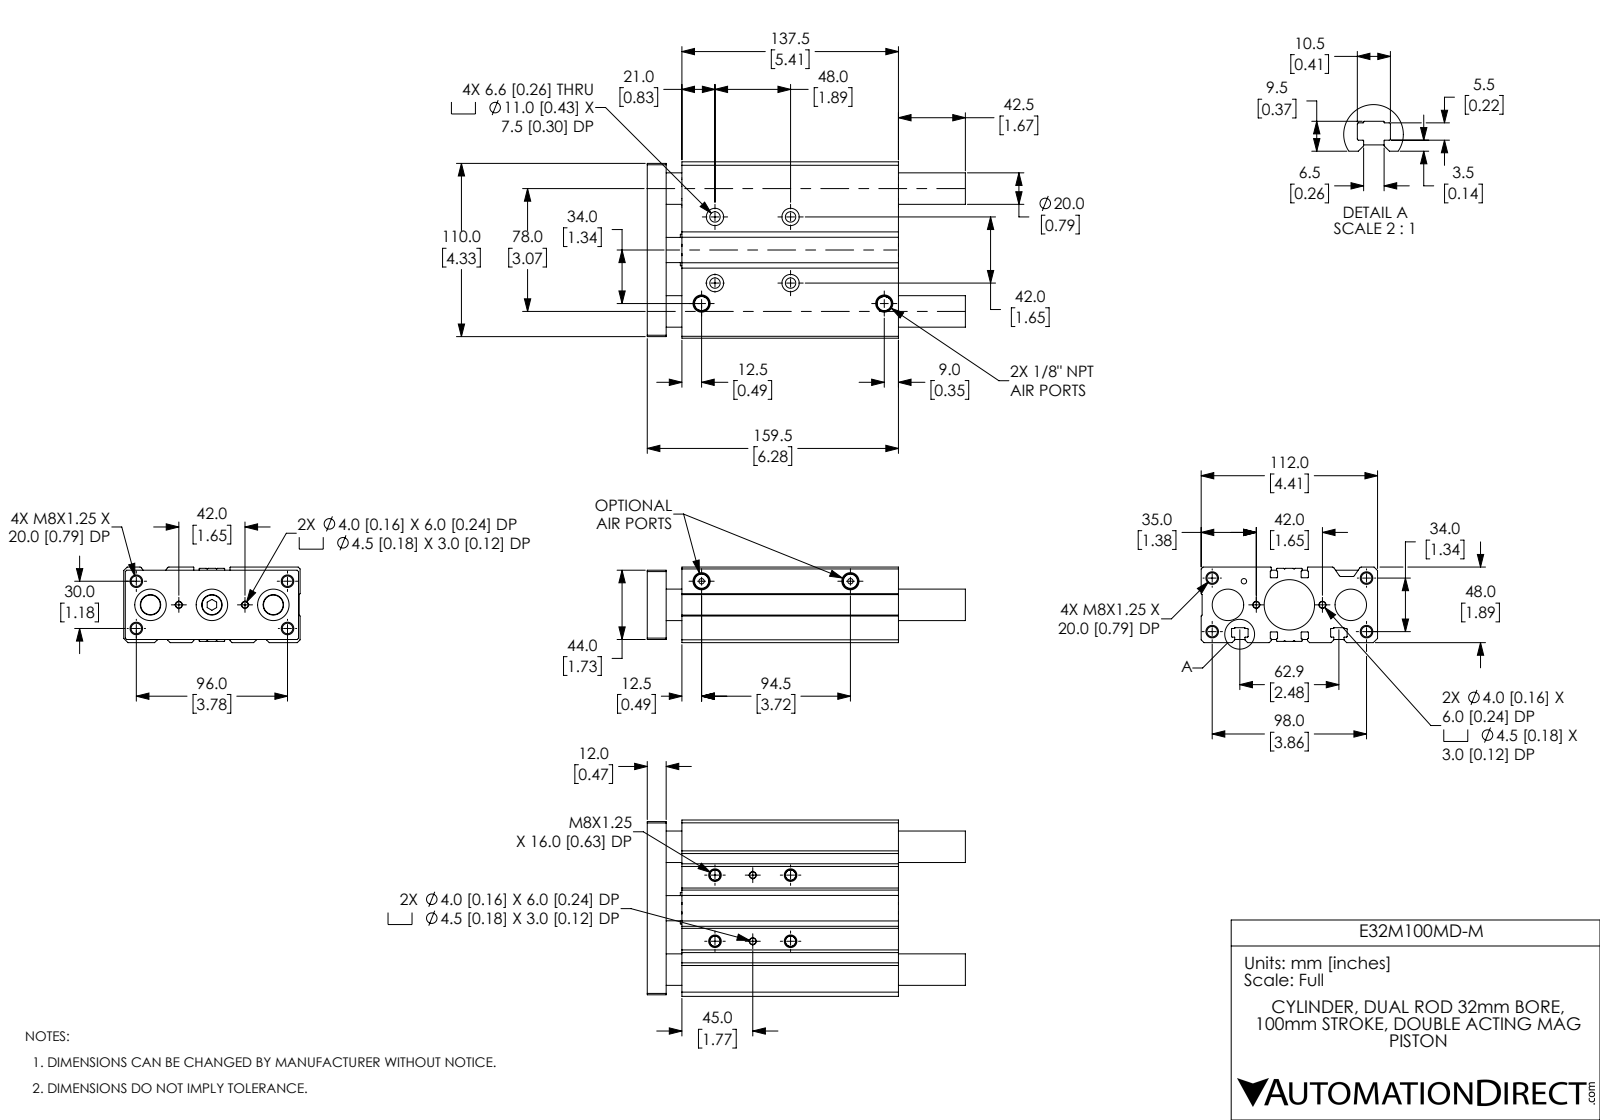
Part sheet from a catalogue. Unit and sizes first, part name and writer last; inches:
Units: inches
Overall size (bounding box): 7.953 × 4.409 × 1.89
Round holes (diameter × count): ⌀0.262 ×12, ⌀0.157 ×4, ⌀0.177 ×4, ⌀0.26 ×4, ⌀0.433 ×4, ⌀0.394 ×3, ⌀0.787 ×3, ⌀0.135 ×2, ⌀0.51 ×2, ⌀0.135 ×1, ⌀0.787 ×1, ⌀1.26 ×1
Round bosses / shafts (diameter × count): ⌀0.63 ×1, ⌀0.51 ×1
Partial cylindrical surfaces — rounded edges, fillets, slot ends (radius × count): R0.008 ×32, R0.016 ×28, R0.047 ×4, R0.012 ×2
Main face-to-face distances: 1.89, 0.236, 0.031, 4.409, 0.866, 0.472, 0.394, 1.858, 0.079, 6.28
Hole centre spacings: 0.088, 0.689, 0.776, 0.945, 1.216, 1.261, 1.29, 1.654
Volume: 42.39 in³ · Surface area: 246.8 in²
Bodies: 5 solids, 423 faces (139 planar, 190 cylindrical, 94 other)
Part name (STEP PRODUCT): E32M100MD-M_BODY; E32M100MD-M; E32M100MD-M_ENDPLATE
STEP written by: SolidWorks 2019 (CONFIG_CONTROL_DESIGN)
